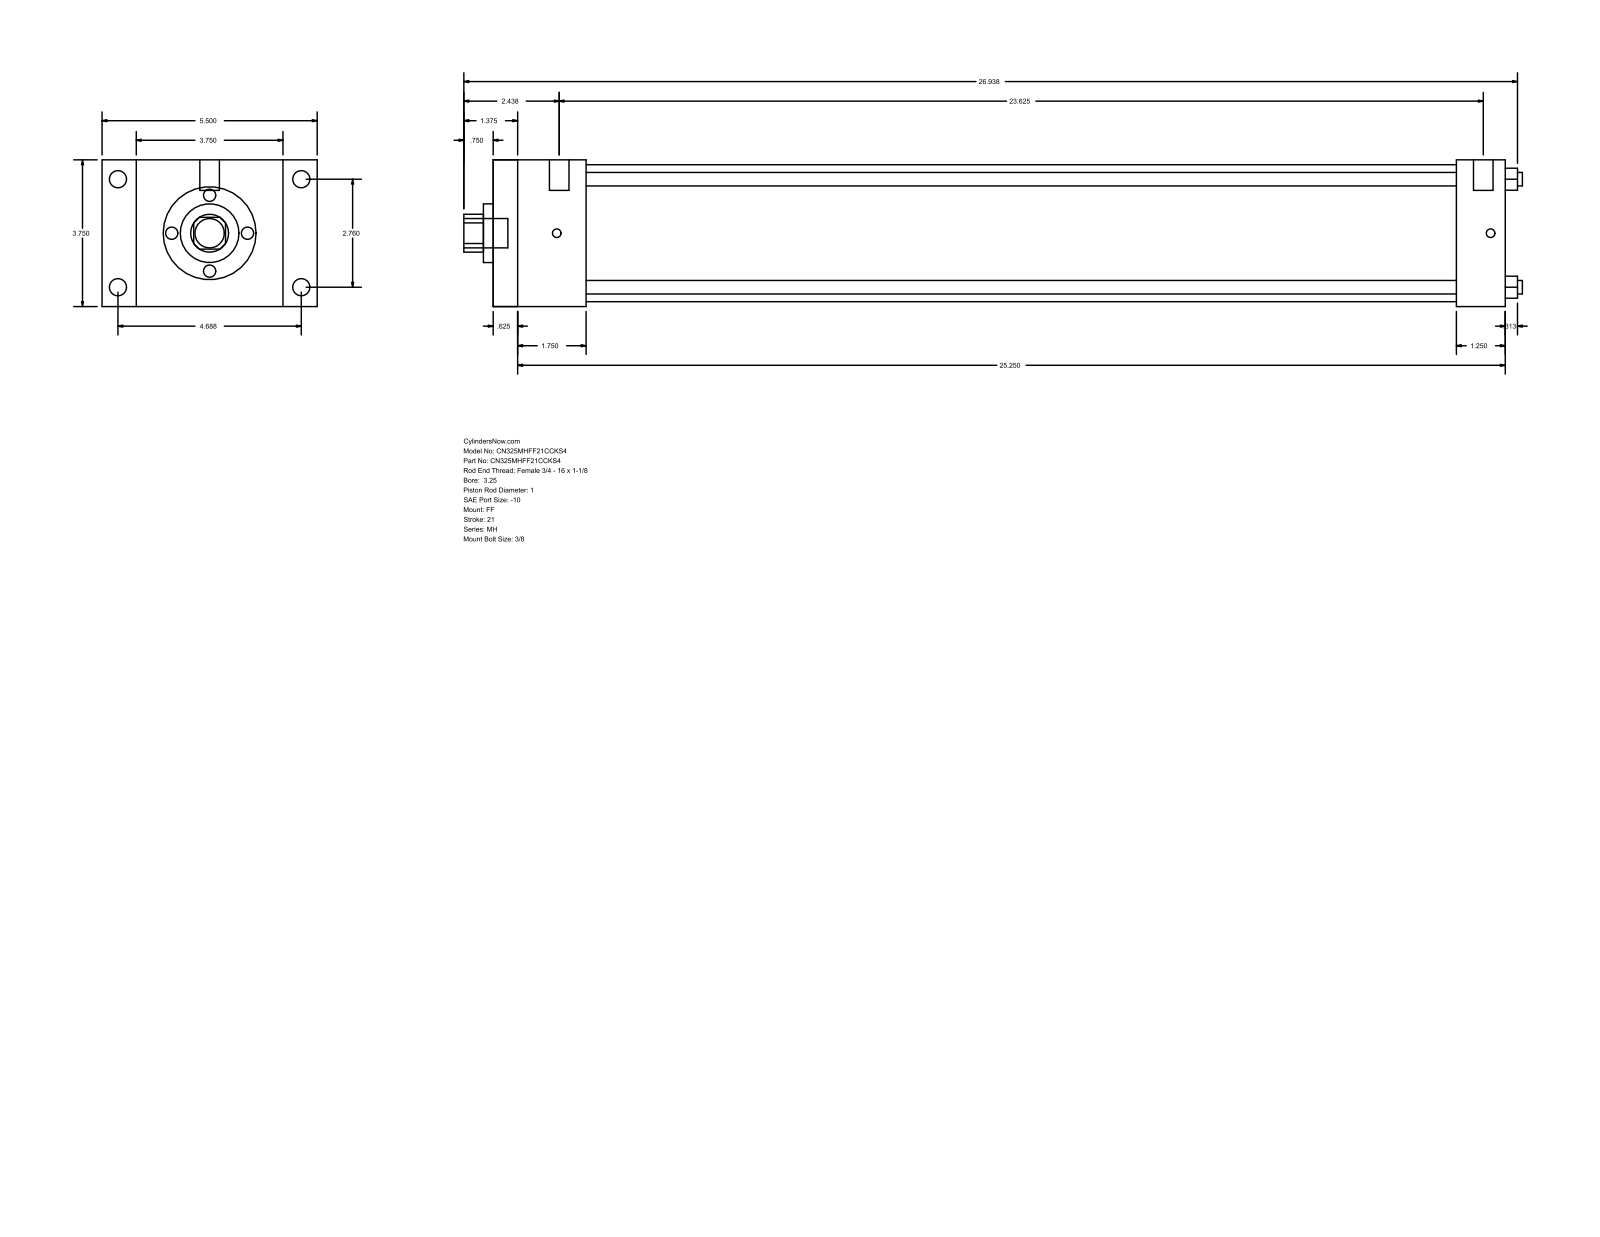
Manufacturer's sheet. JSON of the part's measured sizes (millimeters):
{"part_name": "MH_FF__0325_1", "step_written_by": "GSSL Pune (CONFIG_CONTROL_DESIGN)", "units": "millimeters", "bodies": {"solids": 0, "faces": 92, "planar": 64, "cylindrical": 28, "other": 0}, "overall_size": [687.39, 139.7, 95.25], "round_holes": [[8.76, 4], [25.4, 1], [38.1, 1], [88.9, 1]], "round_bosses_or_shafts": [[11.13, 4], [5.56, 4], [12.7, 2], [19.05, 1]], "partial_cylinders_radius": [[12.29, 1]], "face_to_face_distances": [95.24, 657.22, 15.87, 641.35, 22.23, 117.47, 625.47, 609.6, 31.75, 60.33], "hole_center_spacings": [49.57, 70.1, 99.14]}
